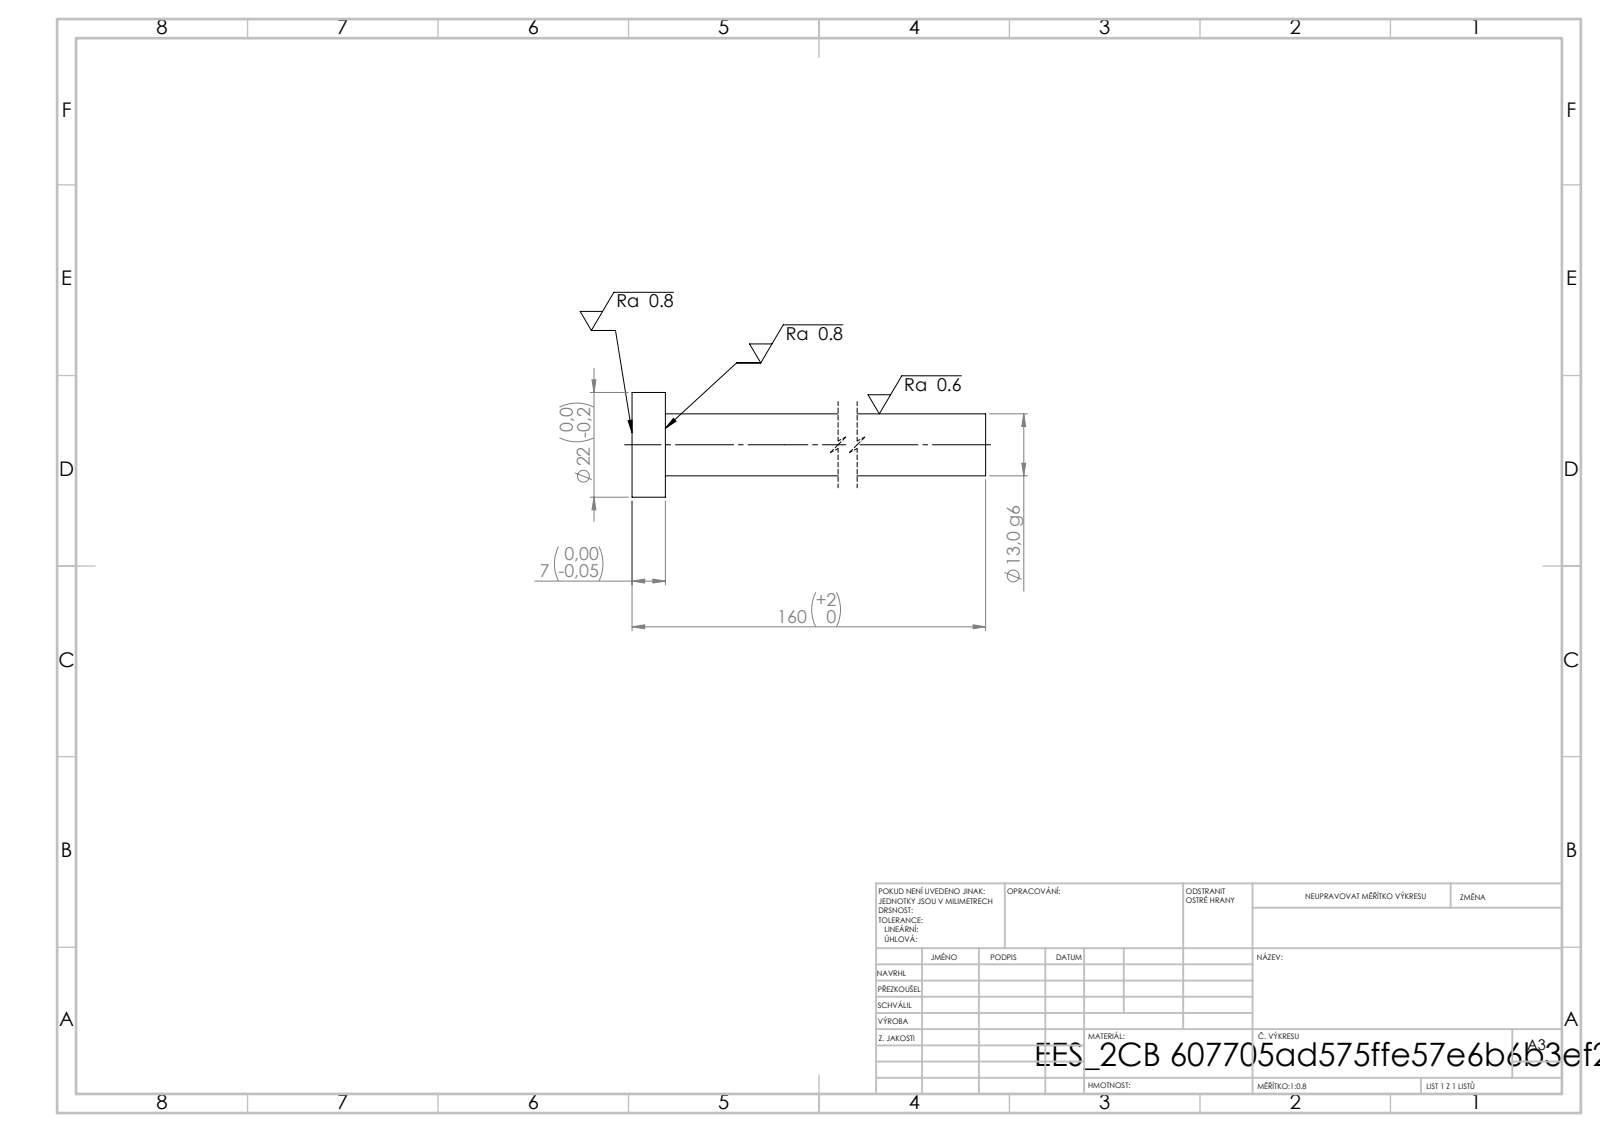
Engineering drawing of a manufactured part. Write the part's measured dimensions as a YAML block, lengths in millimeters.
step_written_by: "SolidWorks 2019 (CONFIG_CONTROL_DESIGN)"
units: millimeters
bodies: {solids: 1, faces: 7, planar: 3, cylindrical: 4, other: 0}
overall_size: [160, 22, 22]
volume: 22969
surface_area: 7493
round_bosses_or_shafts:
  - {diameter: 22, count: 1}
  - {diameter: 13, count: 1}
face_to_face_distances: [7, 160, 153]
